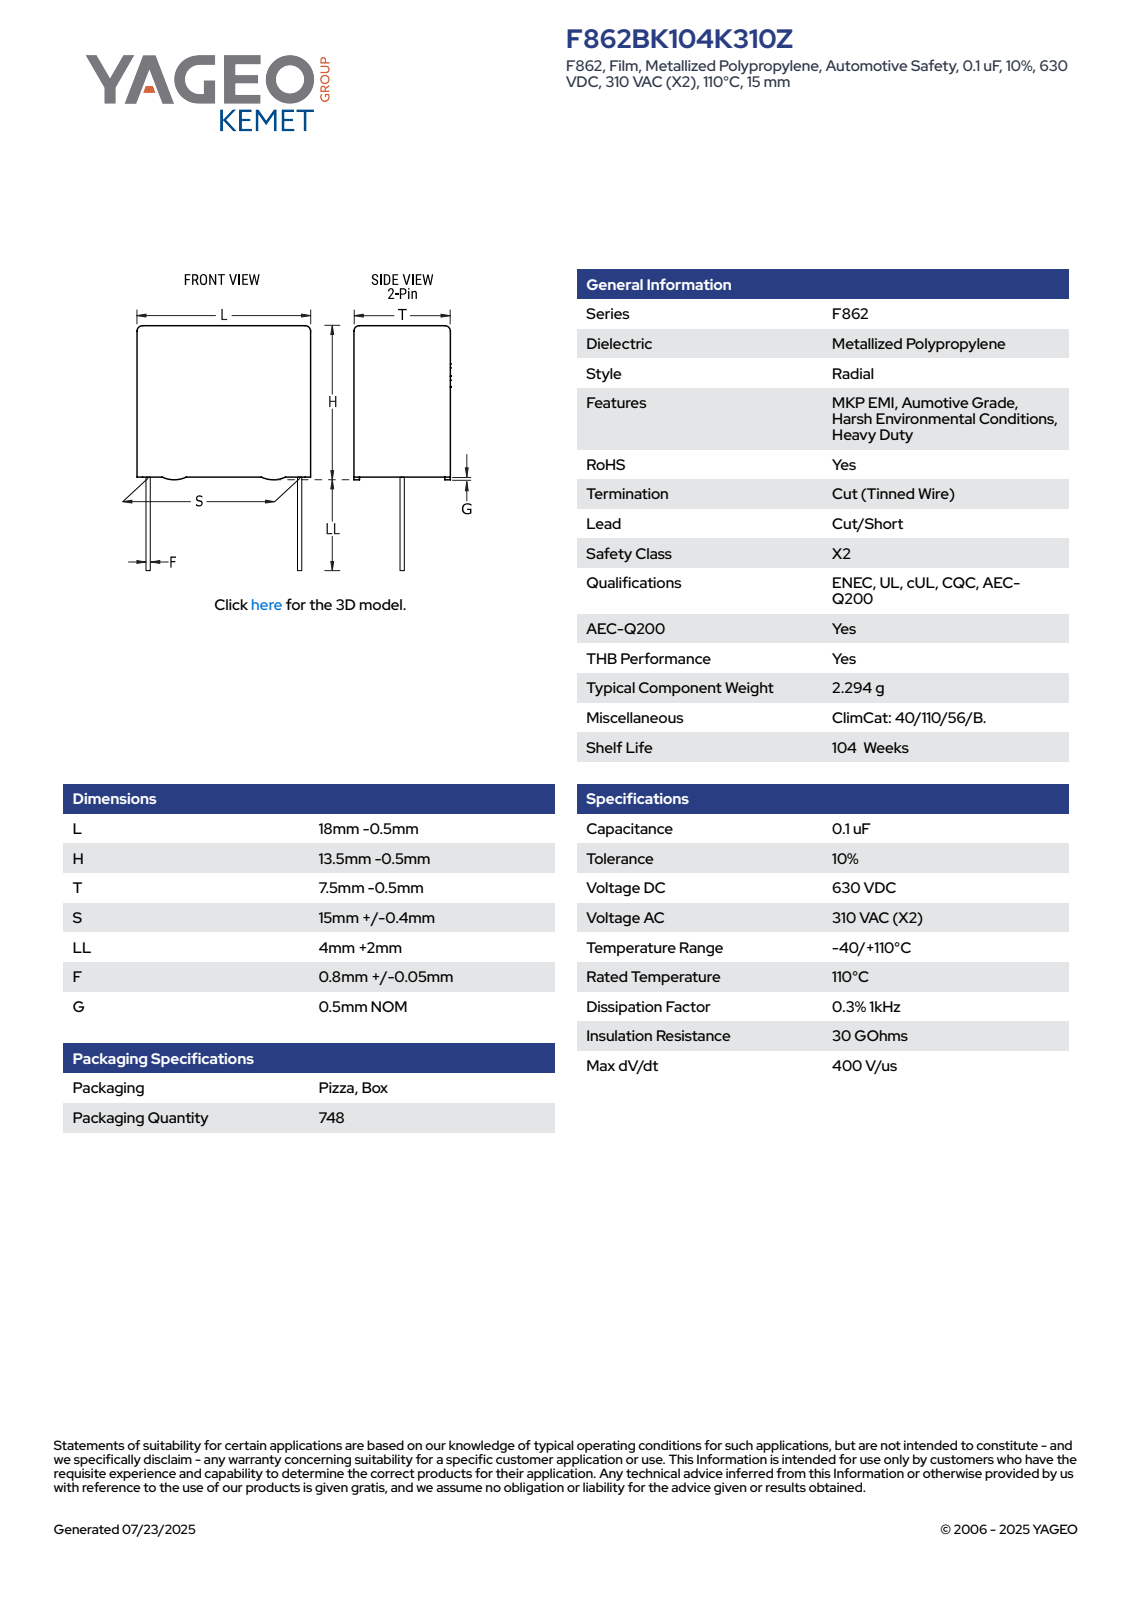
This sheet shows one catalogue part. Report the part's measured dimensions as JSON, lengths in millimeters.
{"part_name": "CFR_RBG_18X13.5X7.5_L17.5H13T7S15LL6F0.85G0.5", "step_written_by": "SolidWorks 2014 (AUTOMOTIVE_DESIGN)", "units": "millimeters", "bodies": {"solids": 4, "faces": 89, "planar": 81, "cylindrical": 8, "other": 0}, "overall_size": [19, 17.5, 7], "volume_mm3": 1538, "surface_area_mm2": 927, "round_bosses_or_shafts": [[0.85, 2]], "partial_cylinders_radius": [[0.5, 4]], "face_to_face_distances": [7, 12.5, 17.5, 6.6, 0.4, 0.5, 13, 6.2, 6, 6.5]}
